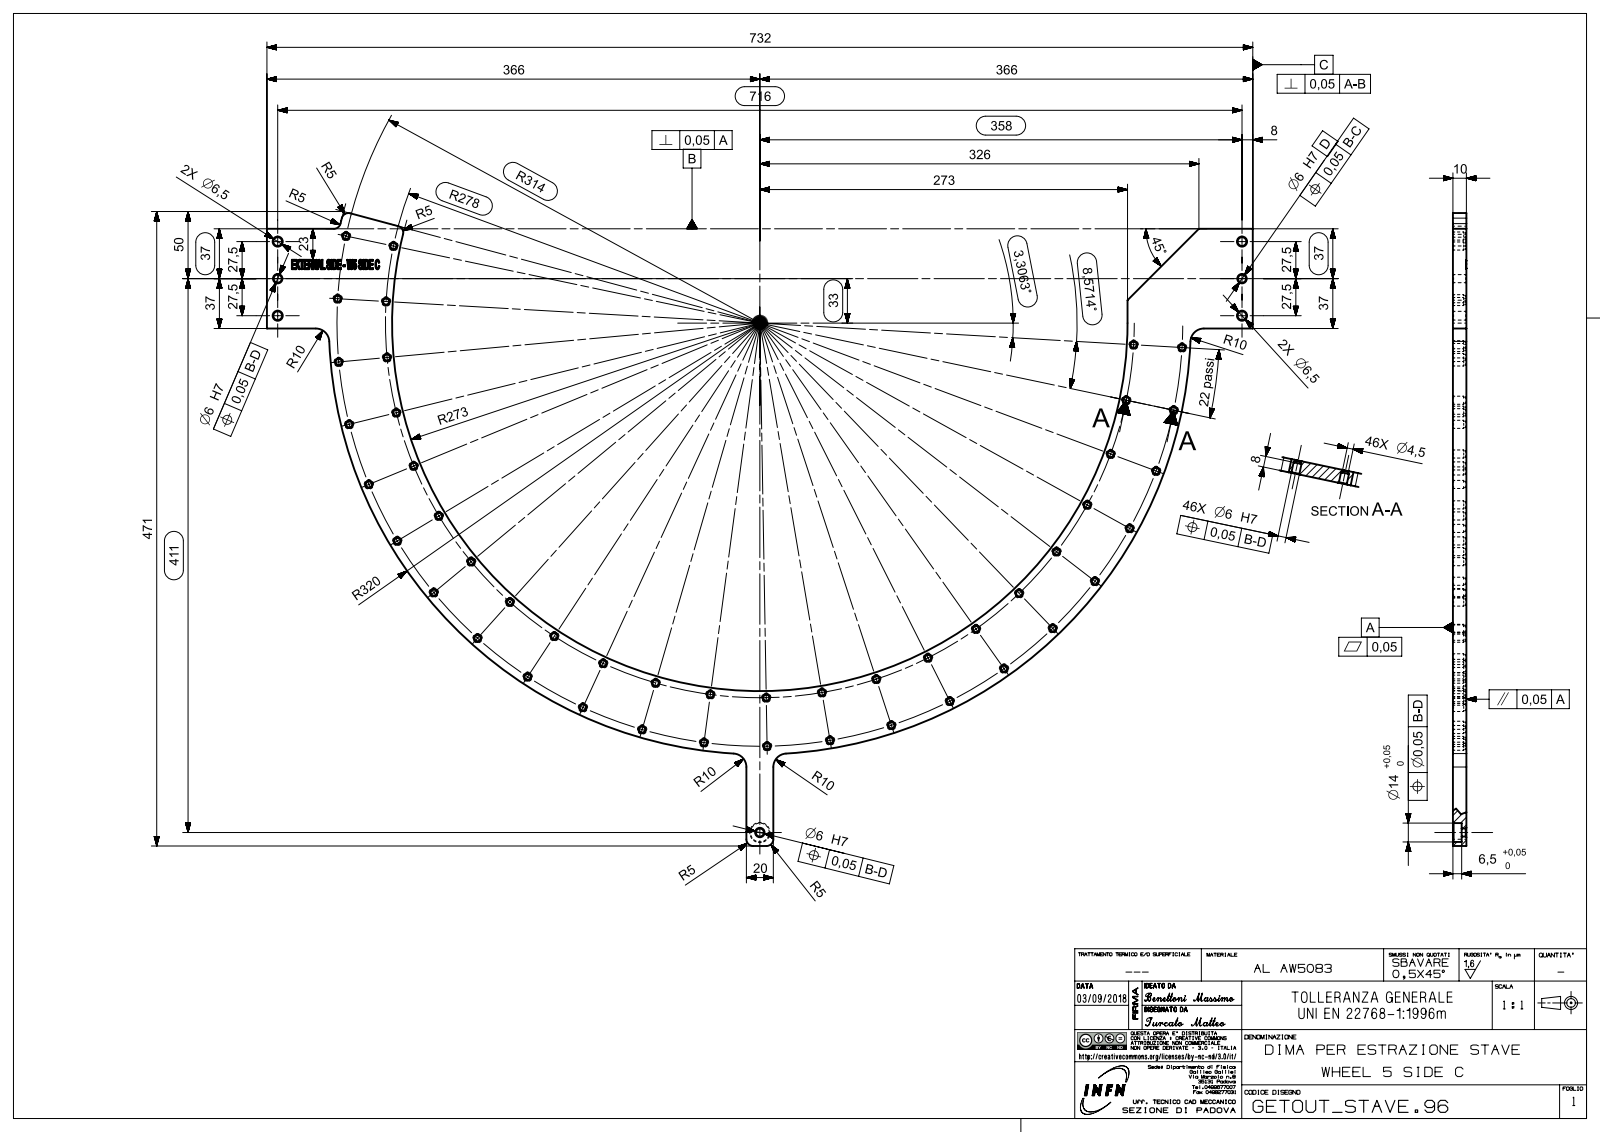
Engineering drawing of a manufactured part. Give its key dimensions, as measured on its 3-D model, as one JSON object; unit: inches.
{"part_name": "bezA730AE56cczm", "step_written_by": "SIEMENS PLM Software NX 12.0 (AUTOMOTIVE_DESIGN)", "units": "inches", "bodies": {"solids": 1, "faces": 473, "planar": 219, "cylindrical": 113, "other": 141}, "overall_size": [28.819, 18.492, 0.394], "volume_in3": 34.3, "surface_area_in2": 229.9, "round_holes": [[0.236, 49], [0.177, 46], [0.256, 4], [0.551, 1]], "partial_cylinders_radius": [[0.197, 5], [0.394, 4], [10.748, 1], [12.598, 1]], "face_to_face_distances": [0.394, 14.016, 14.803, 28.819, 2.913, 0.079, 0.315, 0.787, 0.059, 25.157], "hole_center_spacings": [5.367, 2.243, 3.746, 10.193, 1.848, 7.002, 8.617, 1.417]}
